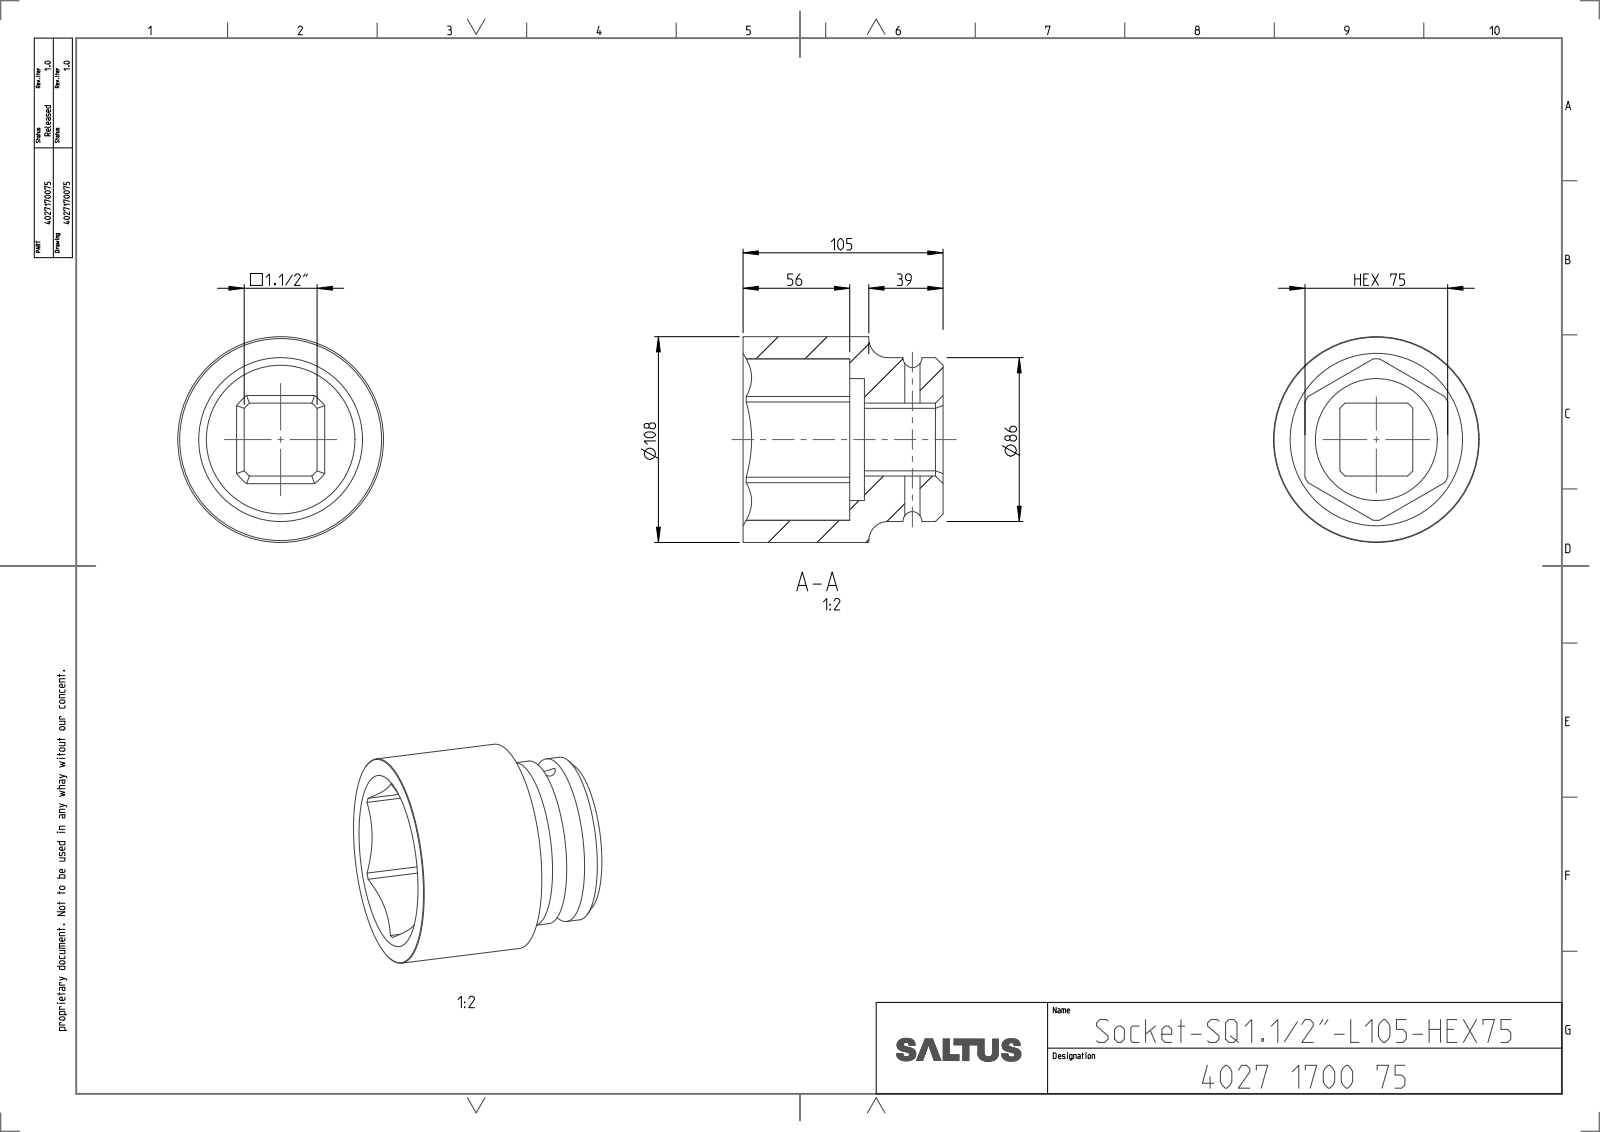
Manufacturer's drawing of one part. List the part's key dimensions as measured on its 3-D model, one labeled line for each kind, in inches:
Part name (STEP PRODUCT): 4027170075
STEP written by: CREO PARAMETRIC BY PTC INC, 2022414 (CONFIG_CONTROL_DESIGN)
Units: inches
Bodies: 1 solid, 55 faces (19 planar, 22 cylindrical, 14 other)
Overall size (bounding box): 4.252 × 4.252 × 4.134
Volume: 28.2 in³ · Surface area: 107.8 in²
Round holes (diameter × count): ⌀0.315 ×1, ⌀2.52 ×1
Round bosses / shafts (diameter × count): ⌀4.252 ×1, ⌀3.386 ×1
Partial cylindrical surfaces — rounded edges, fillets, slot ends (radius × count): R0.992 ×1, R1.669 ×1
Main face-to-face distances: 2.953, 4.134, 0.723, 2.23, 1.507, 1.626, 2.508, 1.929, 0.303, 2.205
